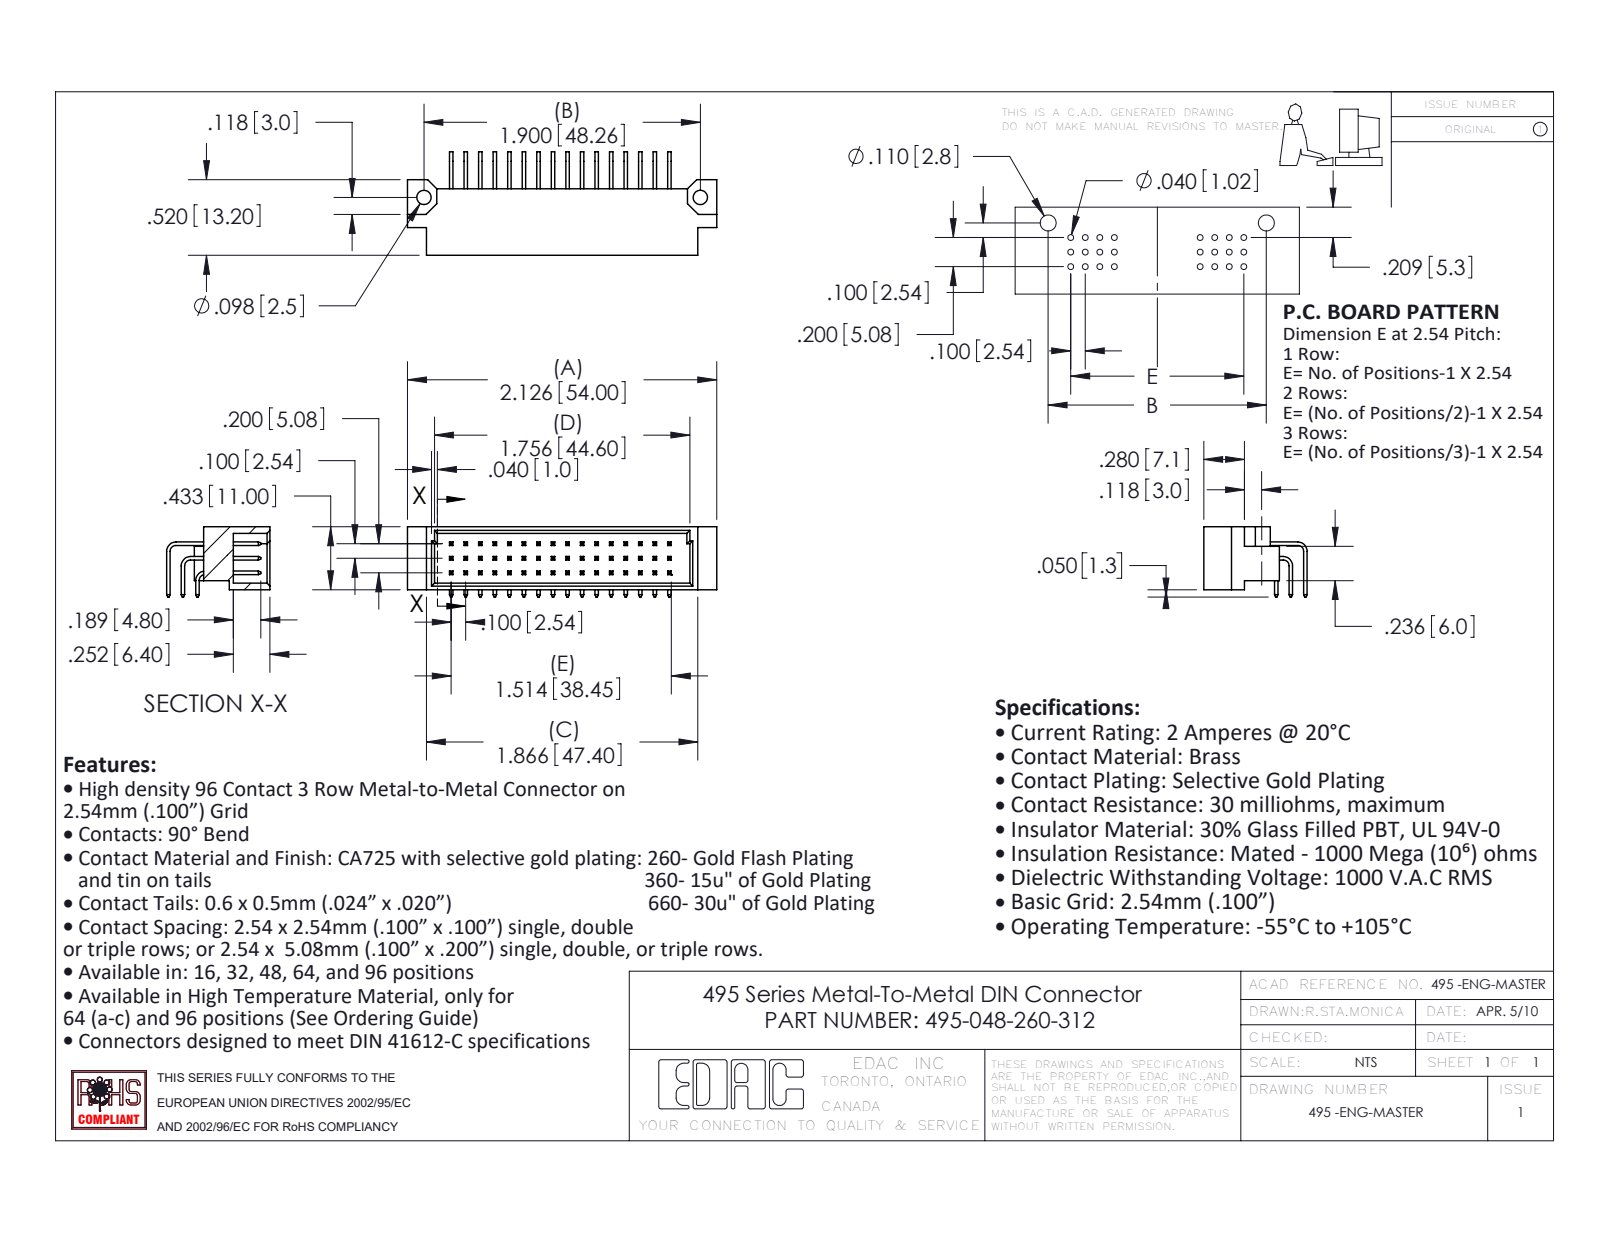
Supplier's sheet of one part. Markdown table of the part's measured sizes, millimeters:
| quantity | value |
| --- | --- |
| part name | 495-290-1; 495-290-3; 495 Part_48; 495-290-2 (+1 more) |
| STEP written by | SolidWorks 2020 (AUTOMOTIVE_DESIGN) |
| units | millimeters |
| bodies | 49 solids, 1106 faces (1006 planar, 100 cylindrical, 0 other) |
| overall size | 54 × 18.05 × 12.27 |
| volume | 3 795 mm³ |
| surface area | 6 262 mm² |
| round holes (diameter × count) | 2.49 × 2 |
| partial cylindrical surfaces (radius × count) | 1.02 × 3, 1.65 × 3 |
| main face-to-face distances | 2.54, 5.08, 0.61, 7.62, 5.2, 10.16, 1.14, 9.86, 12.7, 15.24 |
| hole center spacings | 48.26 |
